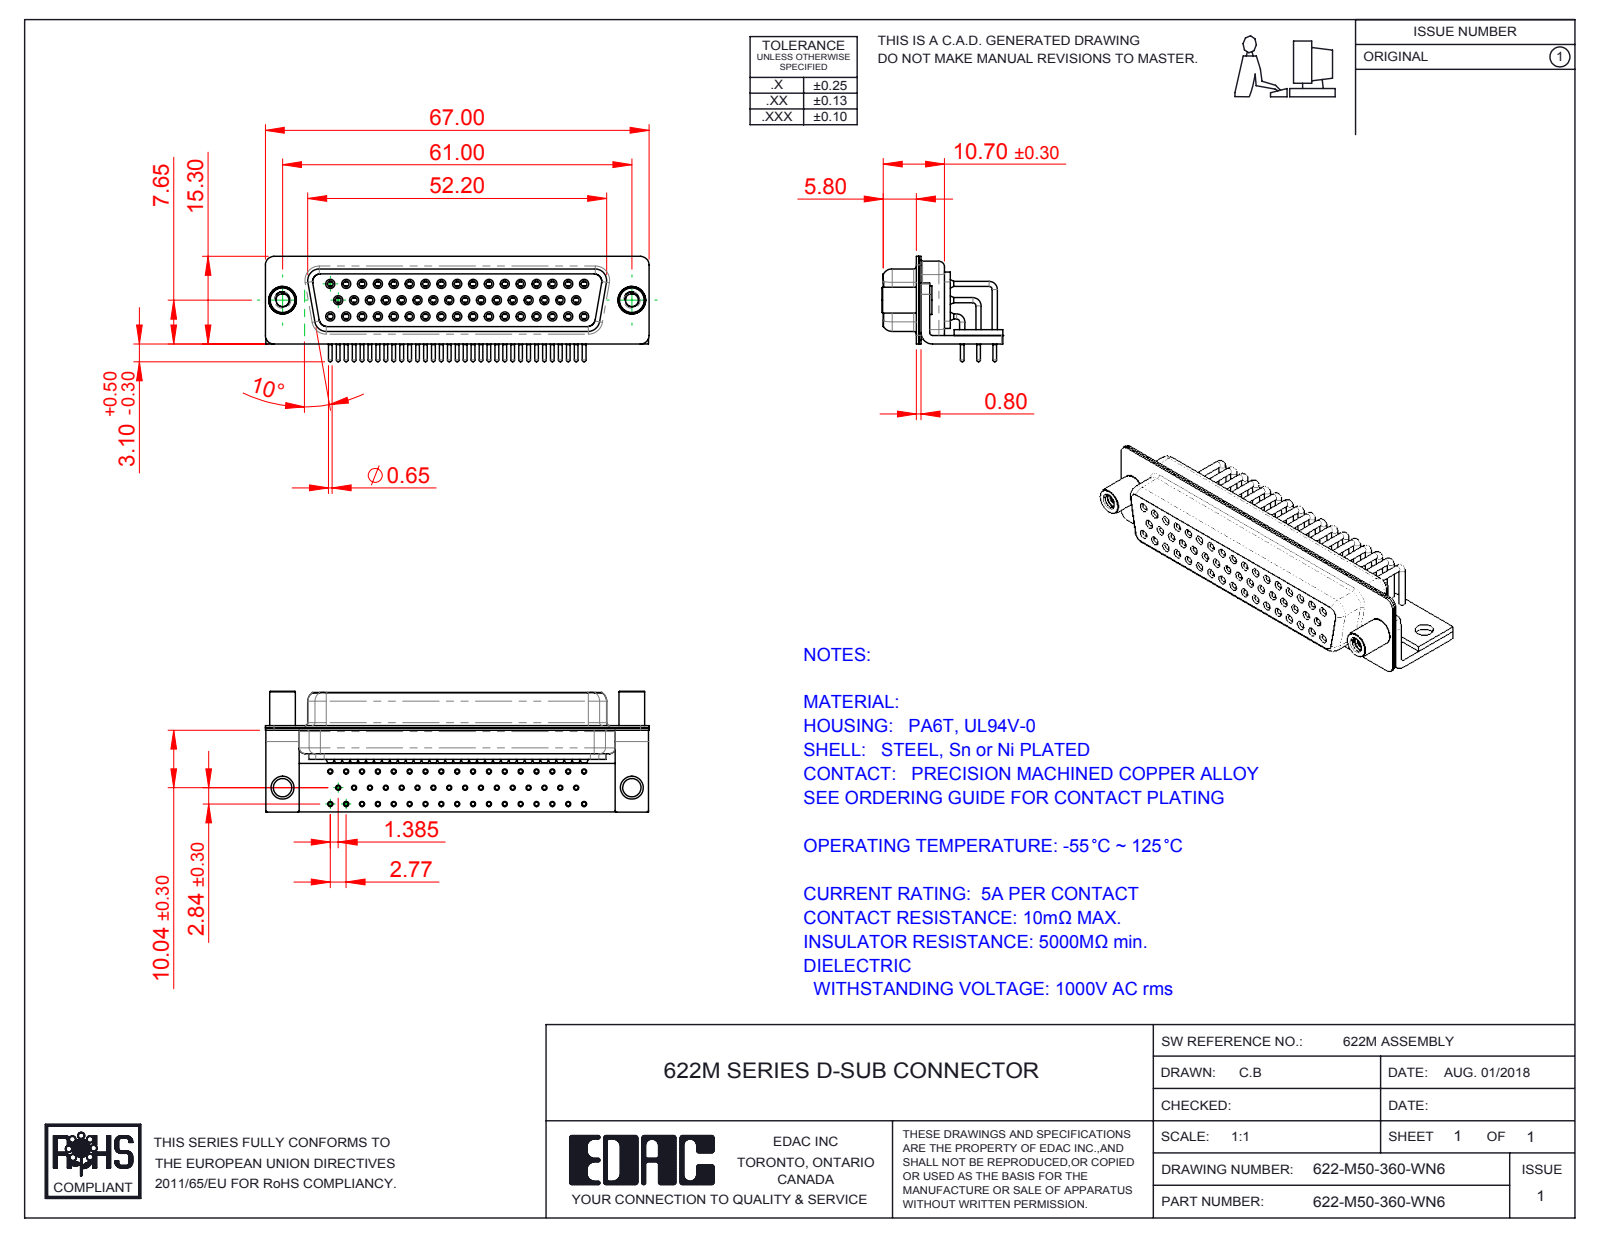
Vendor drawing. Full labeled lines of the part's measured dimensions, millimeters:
Part name (STEP PRODUCT): 622M Stabilizer Board_50 Contacts; 622M 4-40 Threaded Standoff; 622M Stabilizer Bracket_50 Contacts; 622M Contact Row 3 (+6 more)
STEP written by: SolidWorks 2016 (CONFIG_CONTROL_DESIGN)
Units: millimetres
Bodies: 58 solids, 3129 faces (845 planar, 1451 cylindrical, 833 other)
Overall size (bounding box): 67 × 21.1 × 18.4
Volume: 7 871 mm³ · Surface area: 18 434 mm²
Round holes (diameter × count): ⌀0.9 ×50, ⌀1 ×50, ⌀1.1 ×50, ⌀1.7 ×50, ⌀1.8 ×50, ⌀2 ×50, ⌀2.26 ×2, ⌀3.2 ×2, ⌀4 ×2, ⌀4.8 ×2
Round bosses / shafts (diameter × count): ⌀0.9 ×59, ⌀1.6 ×50, ⌀1.5 ×50, ⌀0.65 ×50, ⌀5 ×2, ⌀4.9 ×2, ⌀4.5 ×2
Partial cylindrical surfaces — rounded edges, fillets, slot ends (radius × count): R0.25 ×16, R1.5 ×16, R2 ×13, R1.35 ×8, R1.6 ×8, R0.5 ×5, R0.6 ×4, R0.65 ×4
Main face-to-face distances: 0.4, 1, 2.2, 0.85, 1.35, 11.85, 12.25, 5.8, 0.8, 5.9
Hole centre spacings: 2.77, 3.16, 5.54, 8.31, 11.08, 13.85, 16.62, 19.39
